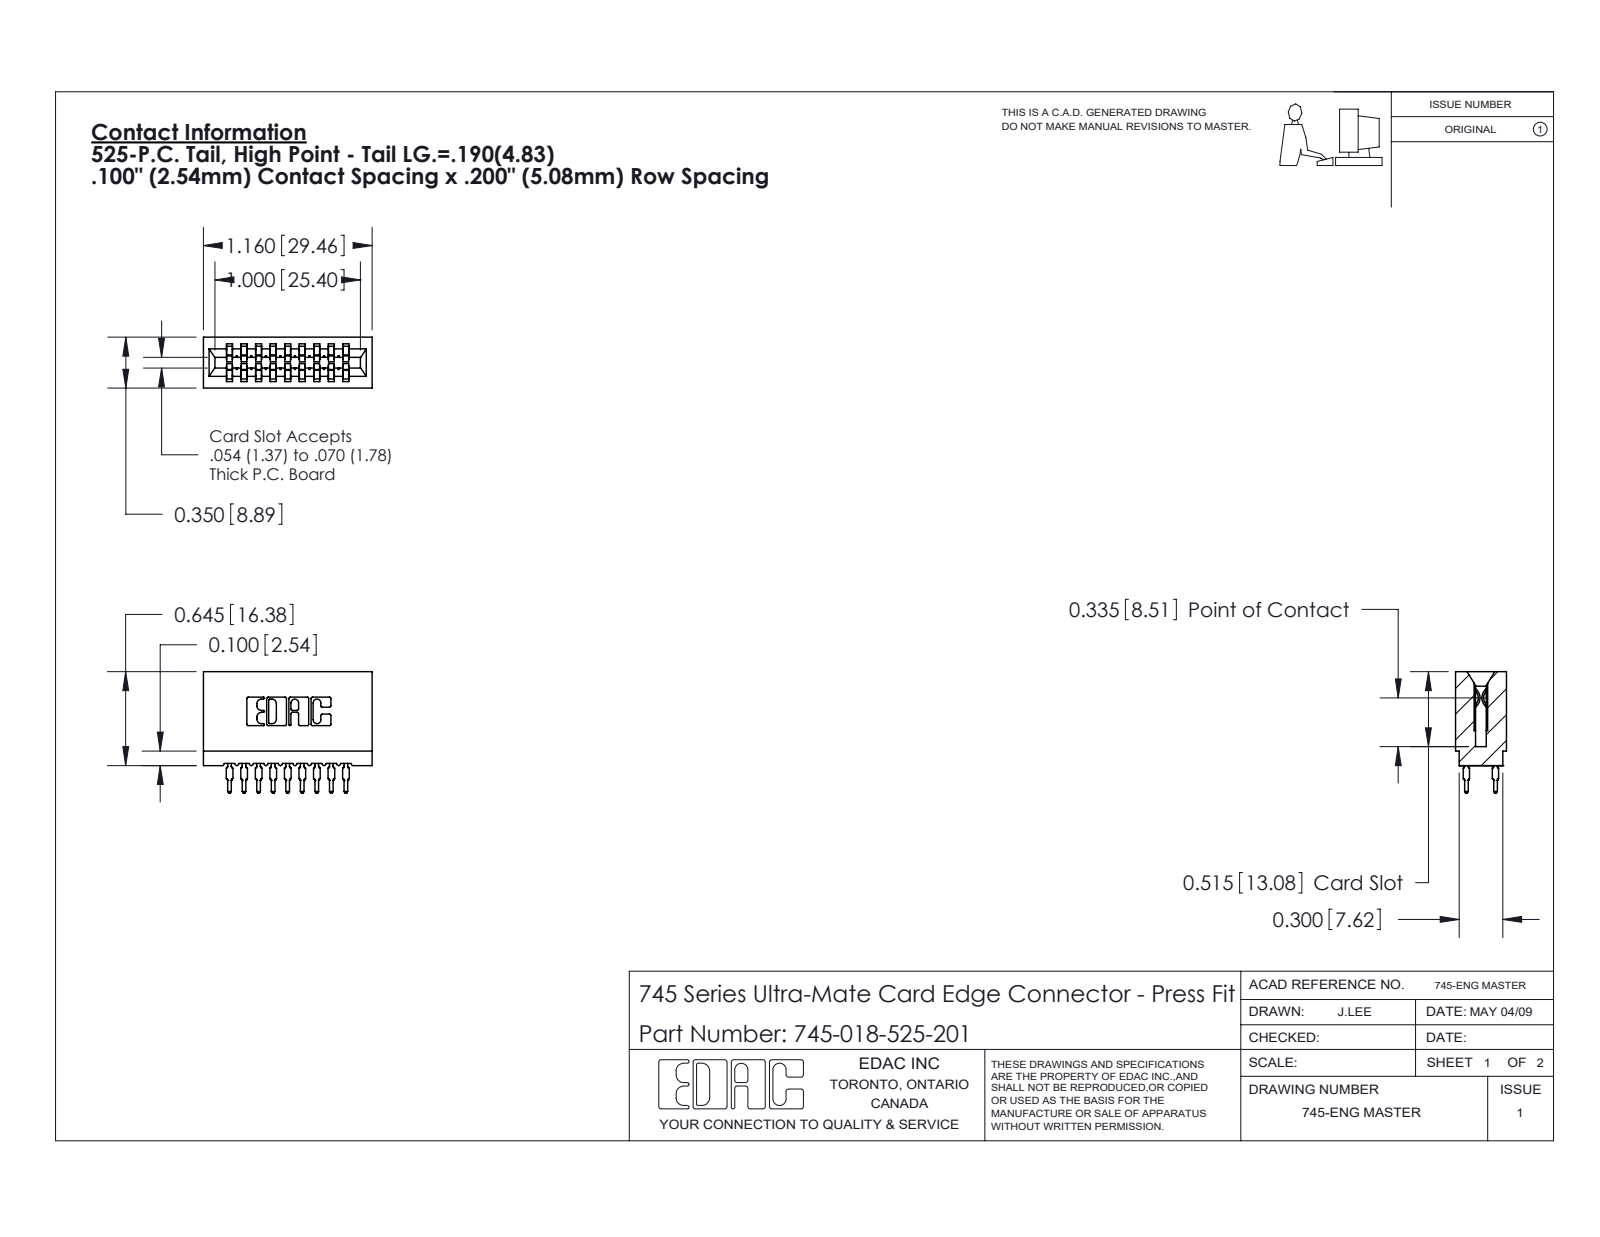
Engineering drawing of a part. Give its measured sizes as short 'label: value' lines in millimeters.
name: 745-018-525-201; 745-292-001_525; 745 Part_Insulator Option - 01
written by: SolidWorks 2020 (CONFIG_CONTROL_DESIGN)
unit: mm
bodies: 19 solids, 1706 faces (883 planar, 355 cylindrical, 468 other)
size: 29.5 × 21.2 × 8.9
volume: 2 850 mm³; area: 5 010 mm²
rounds: 36× R0.5, 22× R0.3, 18× R0.4, 8× R0.1, 8× R0.3, 6× R0.2, 6× R0.8, 3× R0.7
face distances: 2.5, 5.1, 7.6, 10.2, 1.1, 3.6, 12.7, 1.5, 6.1, 4
